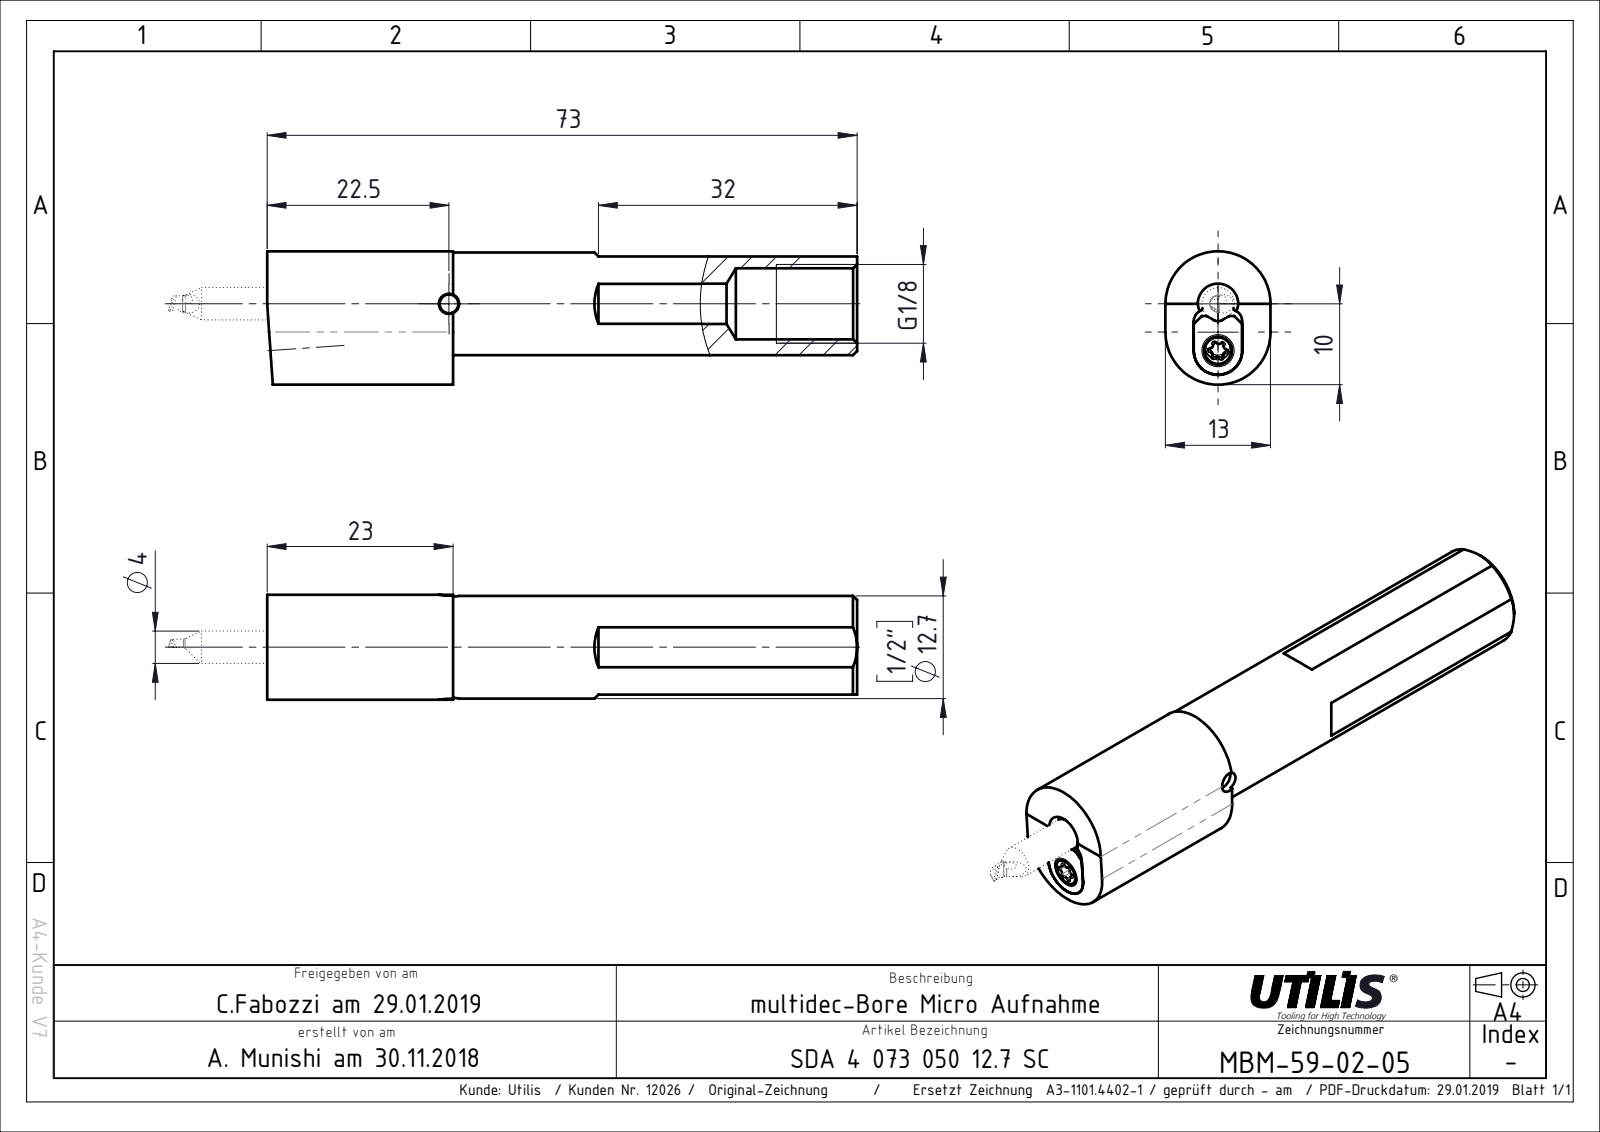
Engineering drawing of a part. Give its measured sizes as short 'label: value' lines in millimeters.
name: MBM-59-02-05
written by: SolidWorks 2018 (CONFIG_CONTROL_DESIGN)
unit: mm
bodies: 1 solid, 49 faces (15 planar, 18 cylindrical, 16 other)
size: 73 × 16.5 × 13
volume: 7 890 mm³; area: 4 911 mm²
holes: 1× ⌀2.5, 1× ⌀3.3, 1× ⌀4, 1× ⌀5, 1× ⌀8.8
bosses: 1× ⌀12.7
rounds: 2× R6.5, 1× R3
face distances: 0.65, 12.35, 13, 3.5, 9.5, 23, 73, 50, 8.85, 6
